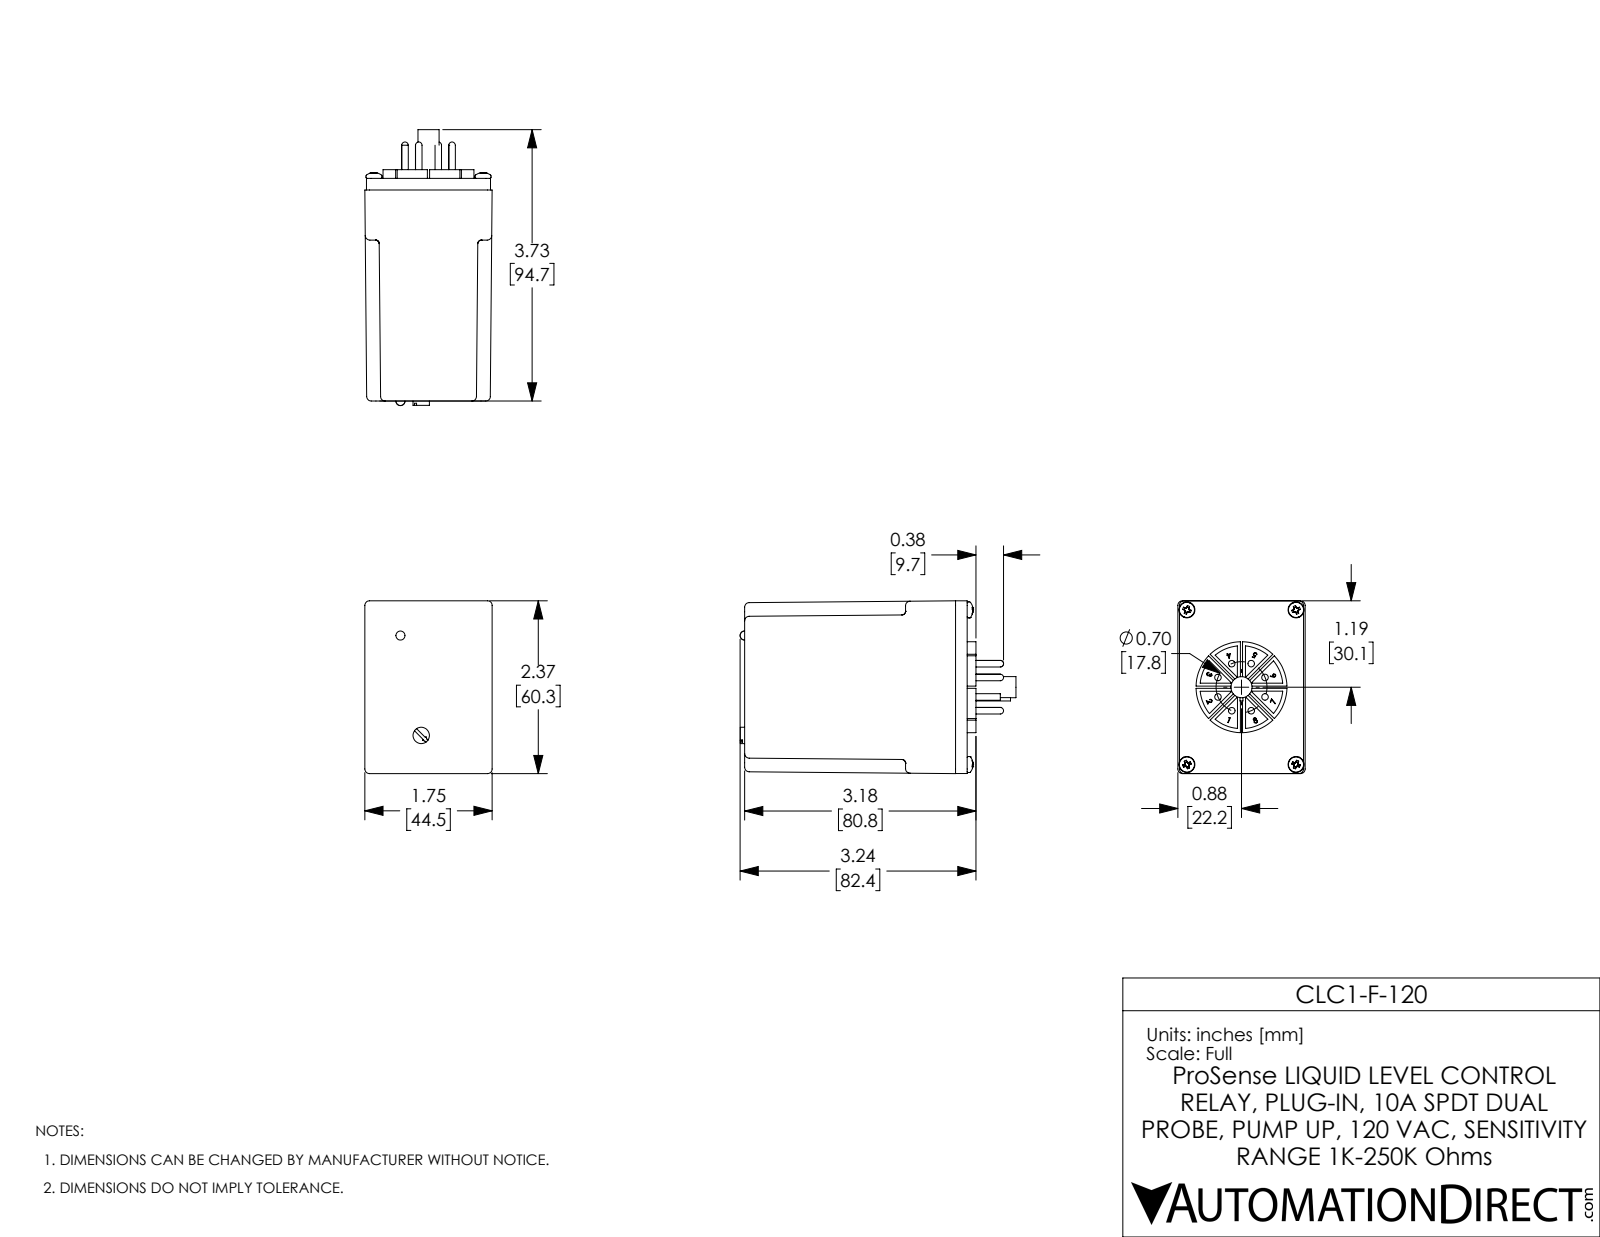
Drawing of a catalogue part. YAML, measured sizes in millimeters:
part_name: "CLC1-F-120"
step_written_by: "SolidWorks 2017 (AUTOMOTIVE_DESIGN)"
units: millimeters
bodies: {solids: 16, faces: 706, planar: 229, cylindrical: 294, other: 183}
overall_size: [96.3, 60.3, 44.5]
volume: 200600
surface_area: 28850
round_holes:
  - {diameter: 3.2, count: 4}
round_bosses_or_shafts:
  - {diameter: 2.3, count: 8}
  - {diameter: 5.6, count: 4}
  - {diameter: 2.8, count: 4}
  - {diameter: 2, count: 4}
  - {diameter: 31.8, count: 1}
  - {diameter: 7.4, count: 1}
  - {diameter: 5.7, count: 1}
partial_cylinders:
  - {radius: 1.6, count: 32}
  - {radius: 0.1, count: 8}
  - {radius: 1.3, count: 4}
  - {radius: 14.5, count: 1}
face_to_face_distances: [73.7, 4.1, 77.7, 1.8, 5.8, 79.5, 4.8, 0.8, 80.8, 1.3]
hole_center_spacings: [38.1, 54, 66.1]
